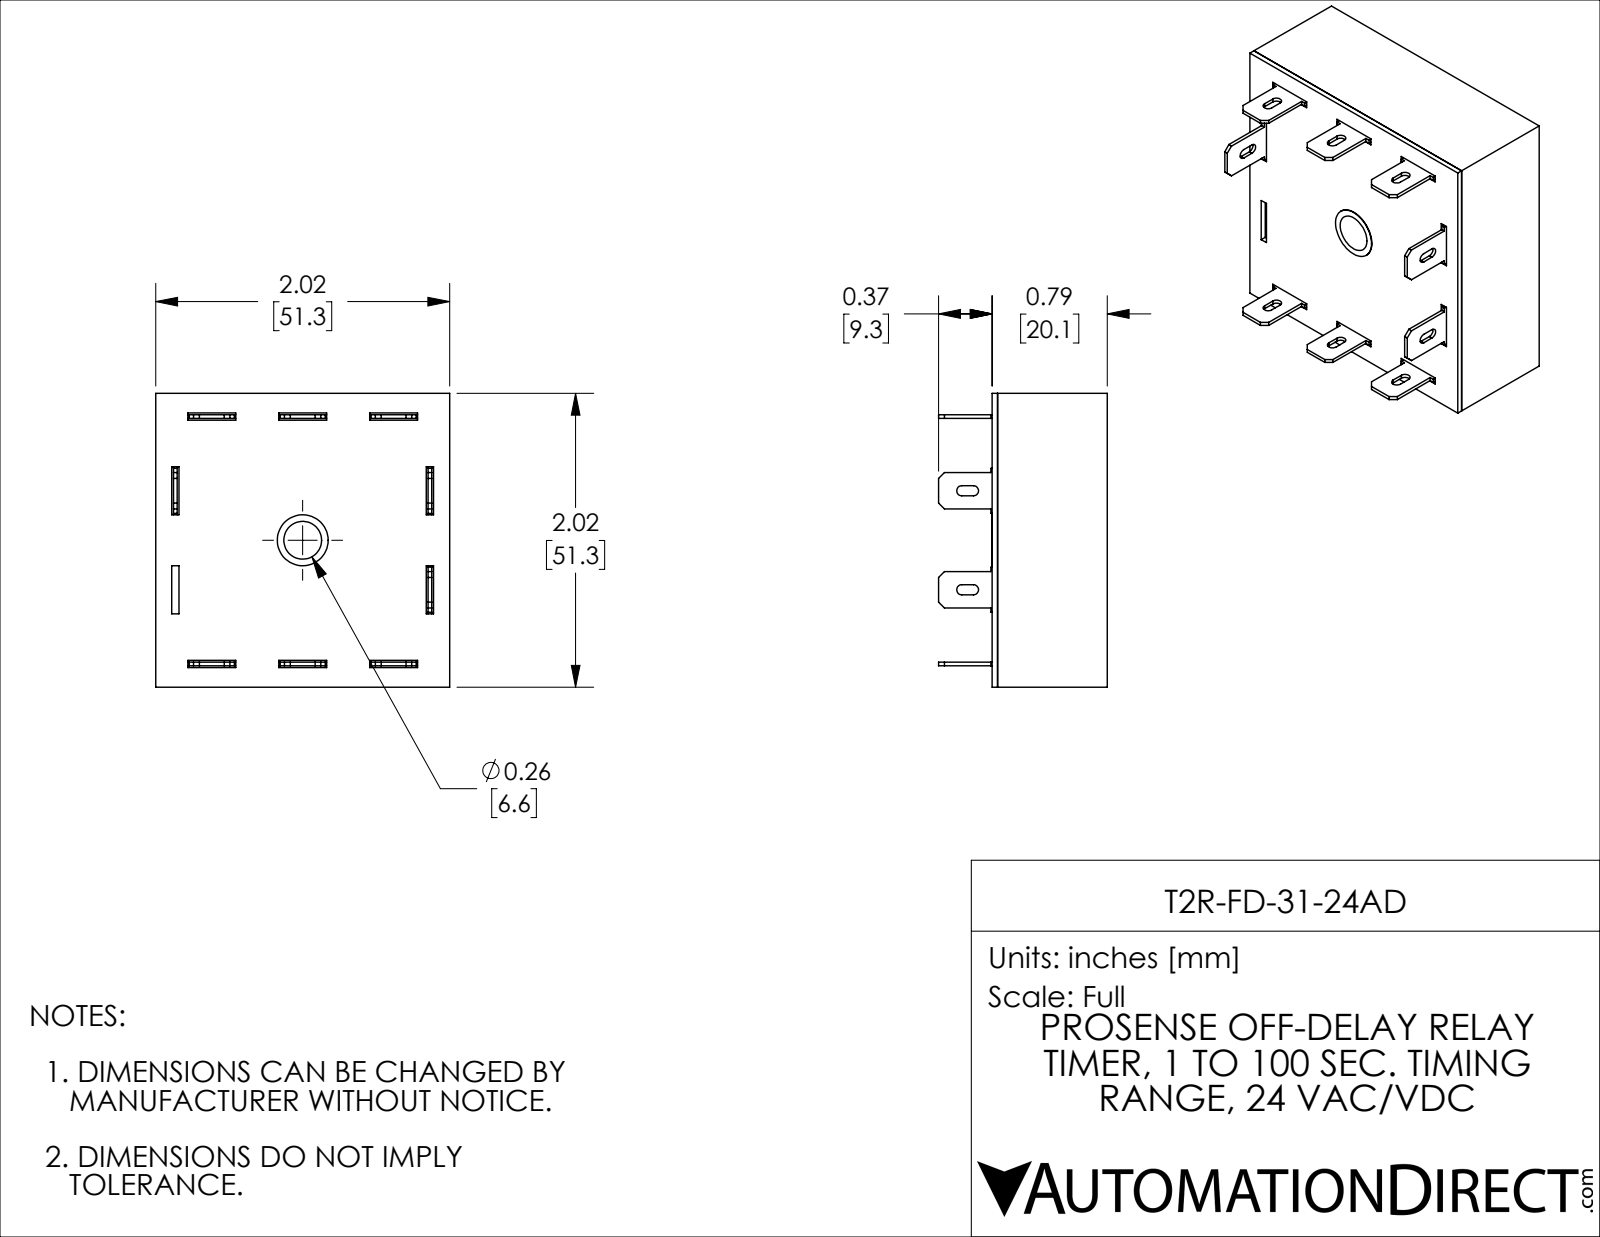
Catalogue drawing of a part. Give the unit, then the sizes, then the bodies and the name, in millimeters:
Units: millimetres
Overall size (bounding box): 51.31 × 51.31 × 29.46
Round holes (diameter × count): ⌀8.89 ×1
Partial cylindrical surfaces — rounded edges, fillets, slot ends (radius × count): R0.89 ×10
Main face-to-face distances: 1.14, 50.16, 19.15, 20.12, 0.97, 18.01, 18.98, 51.3, 3.74, 47.56
Volume: 11 178 mm³ · Surface area: 23 301 mm²
Bodies: 11 solids, 280 faces (256 planar, 22 cylindrical, 2 other)
Part name (STEP PRODUCT): T2R-FD-31-24AD
STEP written by: SolidWorks 2021 (CONFIG_CONTROL_DESIGN)
